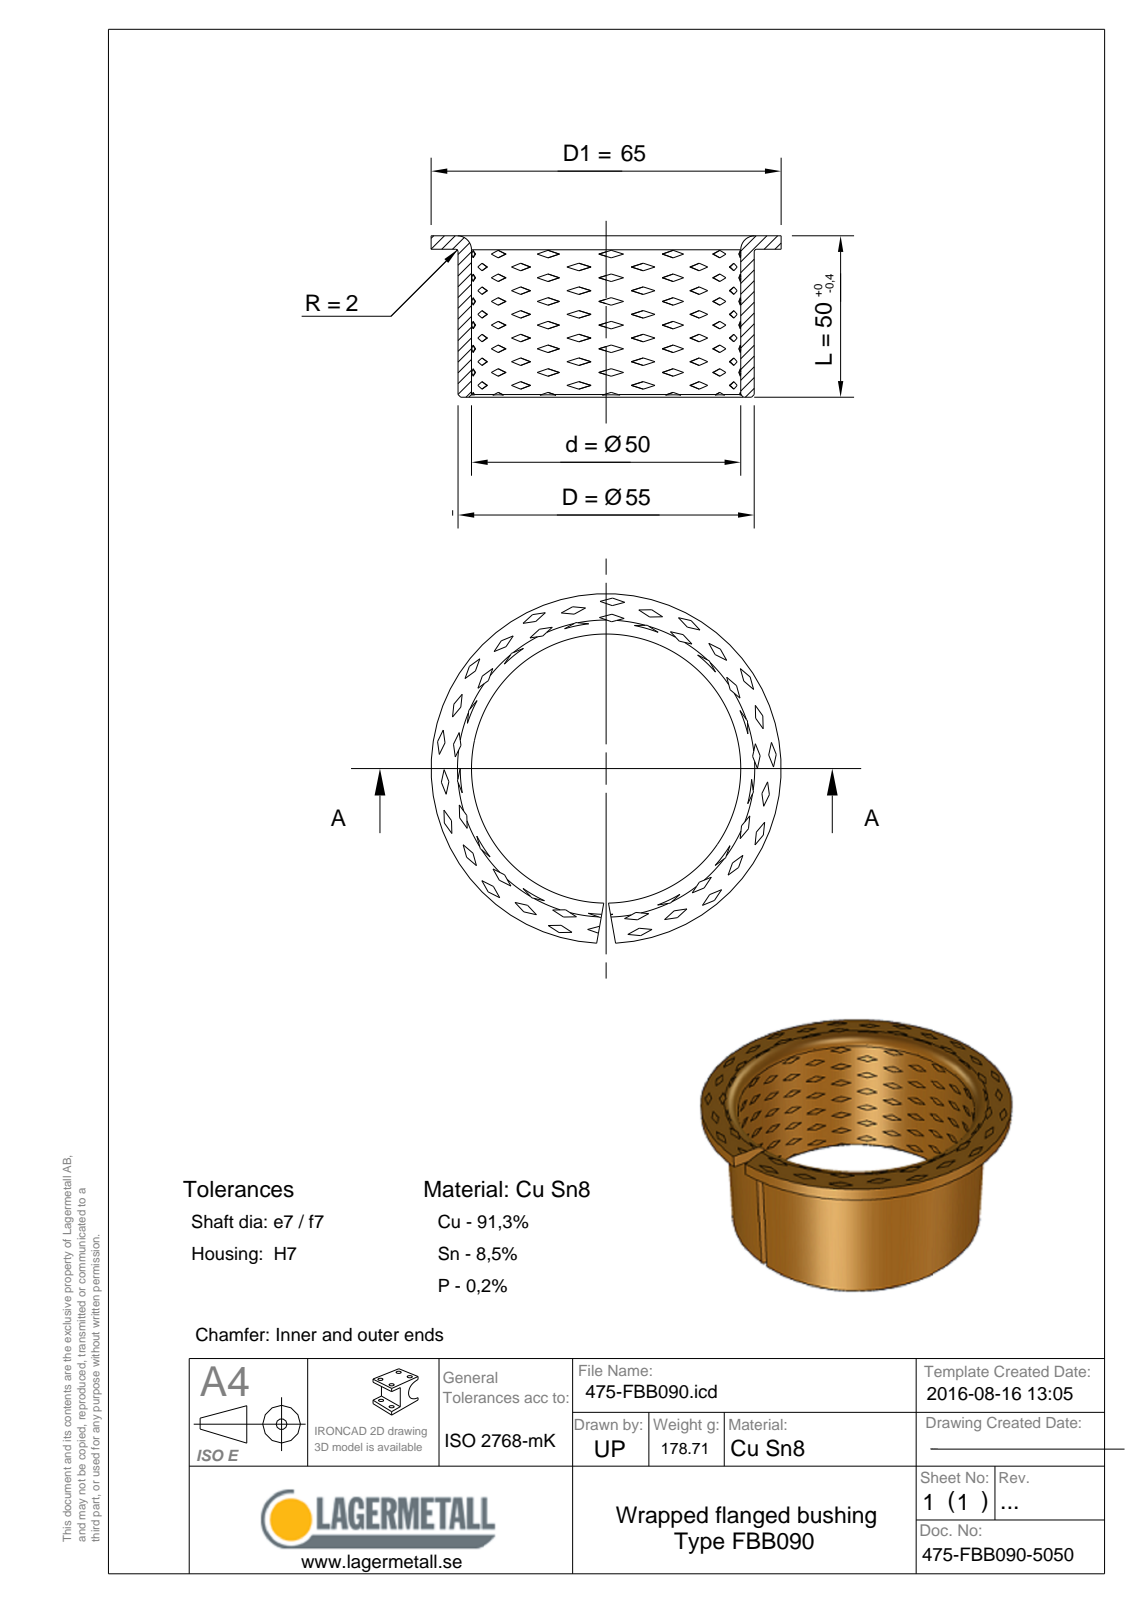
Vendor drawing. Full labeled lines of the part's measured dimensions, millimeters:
Part name (STEP PRODUCT): 475-FBB090-5050
STEP written by: Spatial InterOp 3D (CONFIG_CONTROL_DESIGN)
Units: millimetres
Bodies: 1 solid, 12 faces (5 planar, 3 cylindrical, 4 other)
Overall size (bounding box): 65 × 64.95 × 50
Volume: 22 063 mm³ · Surface area: 18 774 mm²
Round holes (diameter × count): ⌀50 ×1
Round bosses / shafts (diameter × count): ⌀65 ×1, ⌀55 ×1
Main face-to-face distances: 2.5, 47.5, 50
